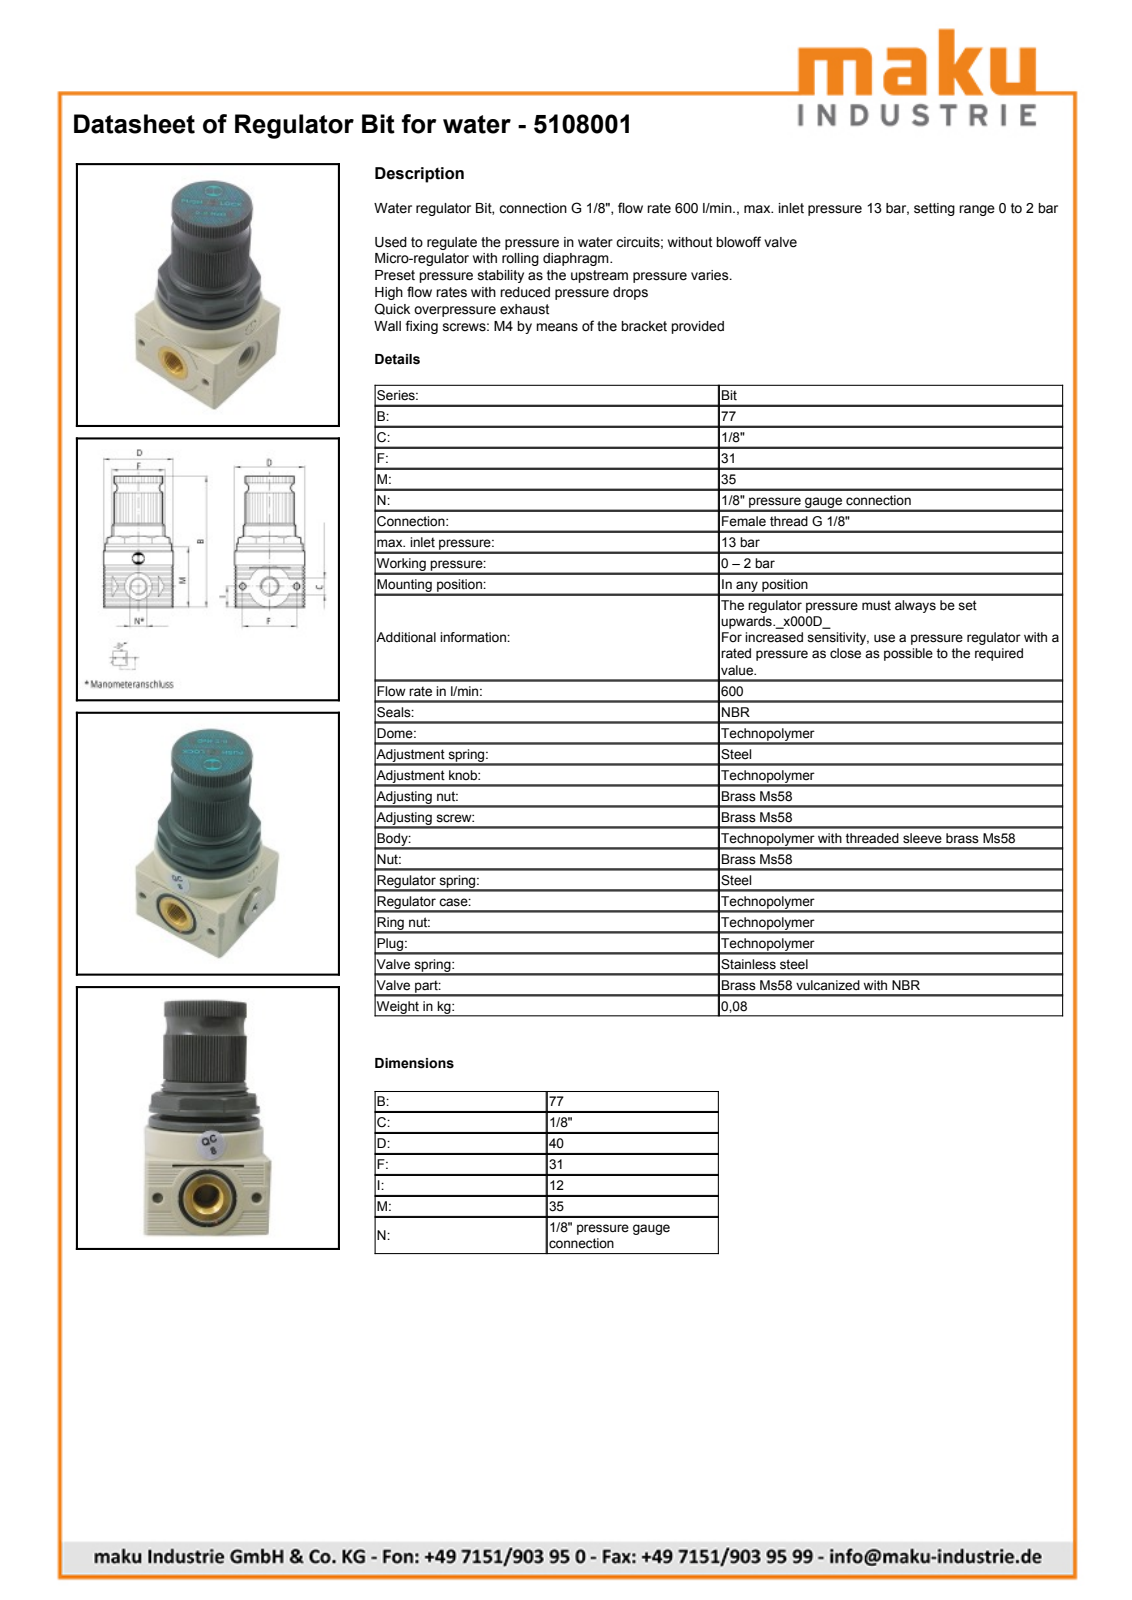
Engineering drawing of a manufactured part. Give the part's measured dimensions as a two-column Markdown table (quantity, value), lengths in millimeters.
| quantity | value |
| --- | --- |
| part name | 5108001; 5108001-BD; 5108001-KN; 1/8-BIT |
| STEP written by | PARTsolutions (AUTOMOTIVE_DESIGN) |
| units | millimeters |
| bodies | 3 solids, 127 faces (92 planar, 27 cylindrical, 8 other) |
| overall size | 77 × 41.5 × 40 |
| volume | 77 227 mm³ |
| surface area | 18 175 mm² |
| round holes (diameter × count) | 4 × 2, 8.57 × 2, 15.5 × 1 |
| round bosses / shafts (diameter × count) | 39.9 × 1, 38 × 1, 37.6 × 1, 30 × 1, 28 × 1, 24 × 1, 15 × 1, 9.73 × 1 |
| partial cylindrical surfaces (radius × count) | 12 × 1 |
| main face-to-face distances | 32, 40, 1, 9, 10, 39.95, 77, 45, 39, 19 |
| hole center spacings | 15.5, 31 |
